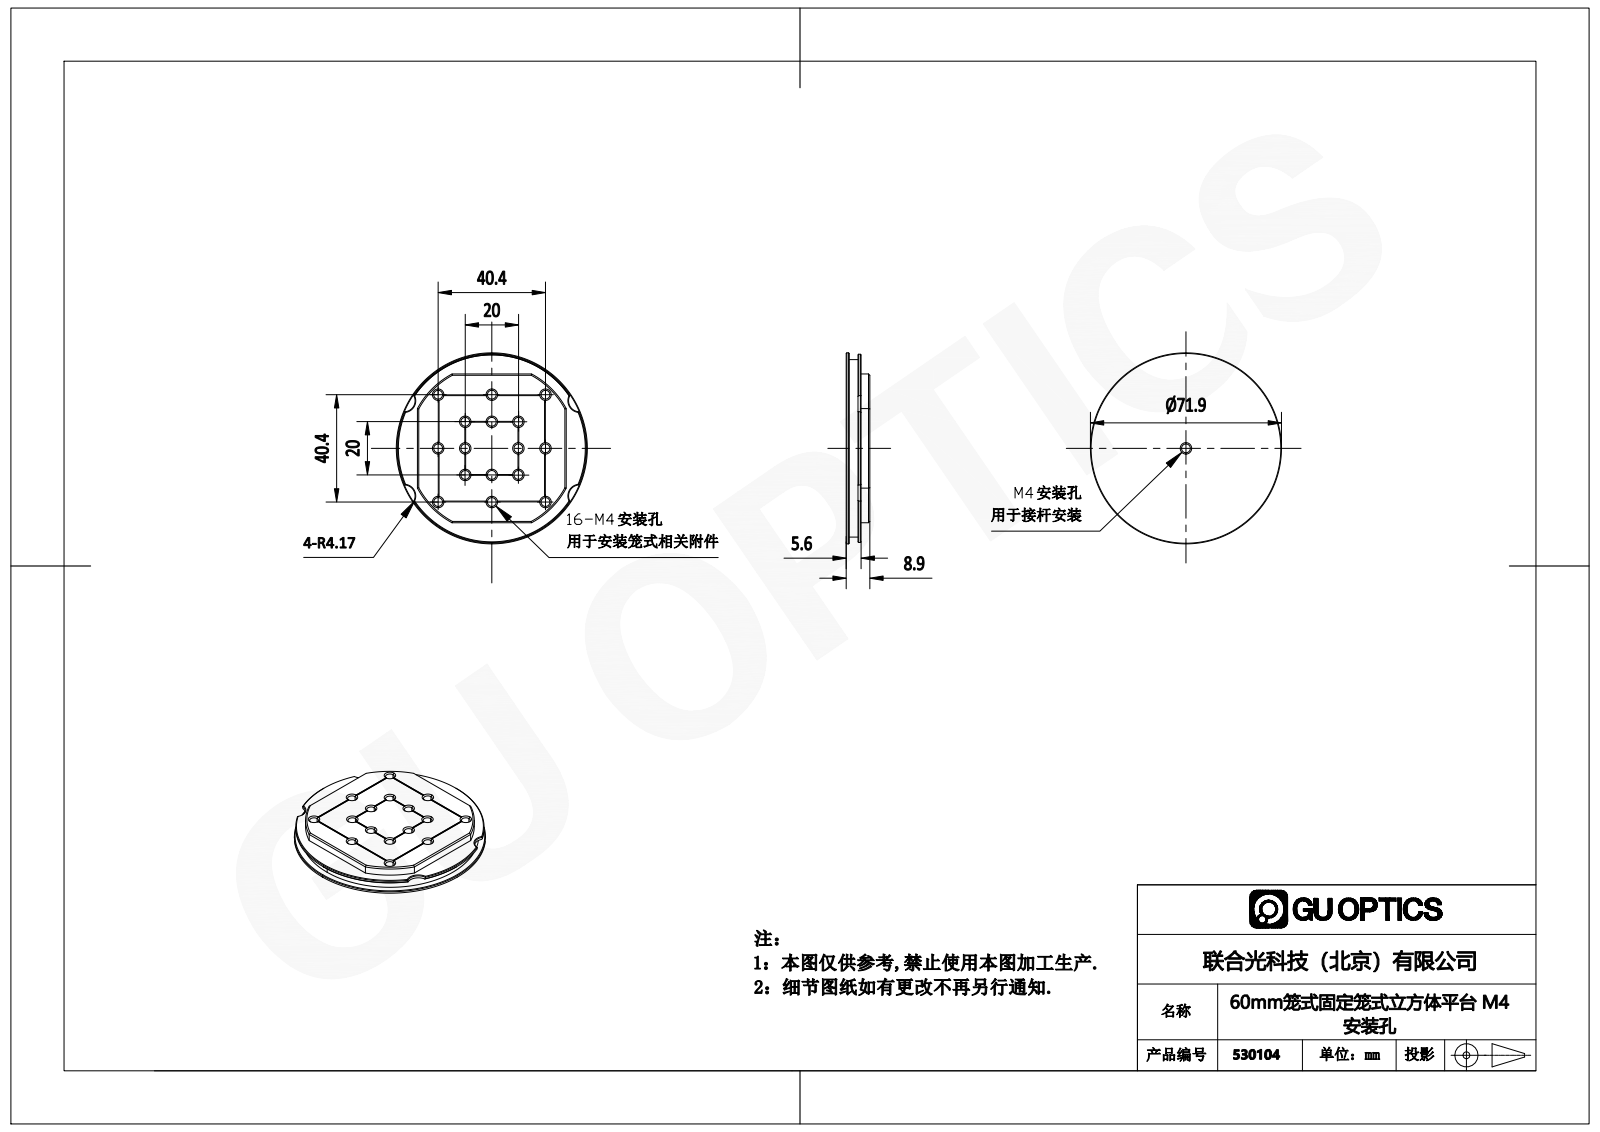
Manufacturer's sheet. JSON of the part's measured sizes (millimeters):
{"part_name": "2.3.7.6_L60F-PM_60 mm笼式固定笼式立方体平台，带M4安装孔", "step_written_by": "SolidWorks 2018 (AUTOMOTIVE_DESIGN)", "units": "millimeters", "bodies": {"solids": 0, "faces": 170, "planar": 63, "cylindrical": 51, "other": 56}, "overall_size": [71.9, 71.9, 8.9], "round_holes": [[3.3, 17]], "round_bosses_or_shafts": [[71.9, 1], [70.86, 1], [66.8, 1]], "partial_cylinders_radius": [[4.17, 4], [31.75, 1]], "face_to_face_distances": [8.9, 3.3, 4.45, 5.6, 1.15, 7.75, 56, 8.89, 7.74, 4.44], "hole_center_spacings": [10, 20.2, 14.14, 14.28, 22.36, 22.54, 22.63, 28.57]}
